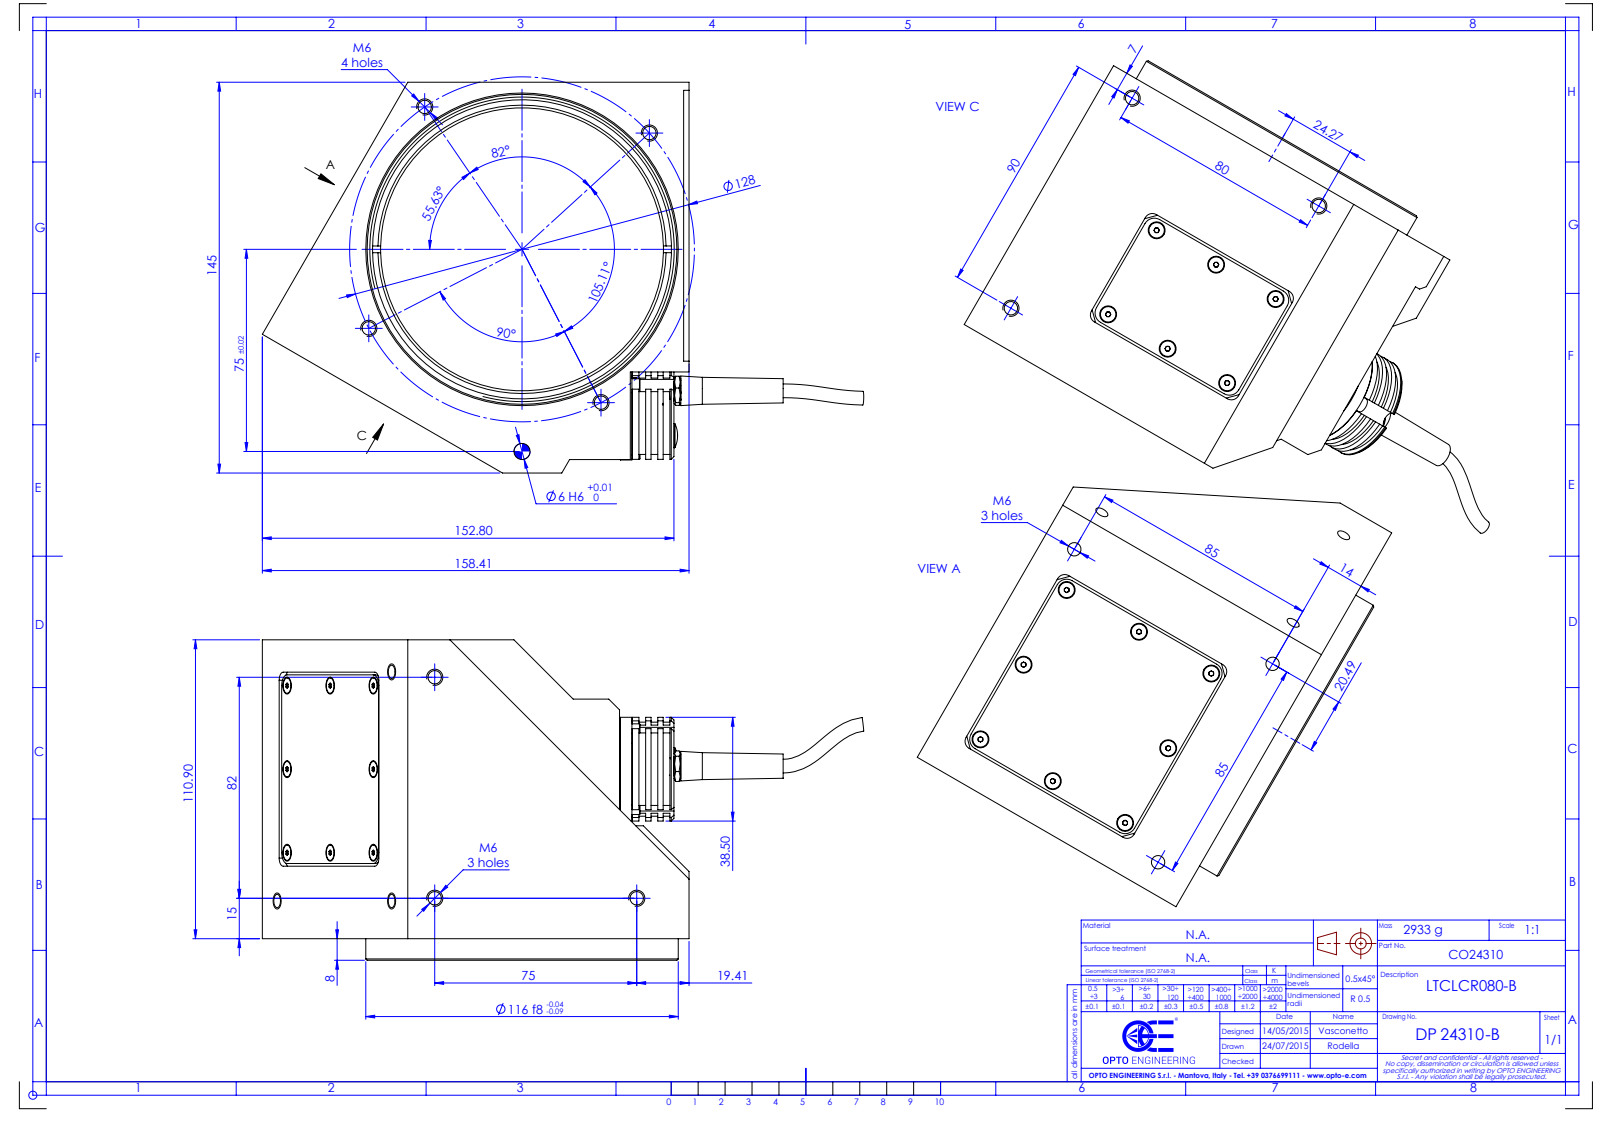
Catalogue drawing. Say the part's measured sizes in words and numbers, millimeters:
The part is named "DP24310-B_LTCLCR080-B". Its 3-D file was written by "SolidWorks 2021 (CONFIG_CONTROL_DESIGN)". It is 0 solids with 404 faces: 156 planar, 138 cylindrical and 110 other. Overall it measures 223.27 by 145 by 118.9 millimeters. Round holes: 13 of diameter 5, 3 of diameter 4, 1 of diameter 6, 1 of diameter 105, 1 of diameter 111. Round bosses or shafts: 18 of diameter 5.75, 3 of diameter 5.5, 1 of diameter 116, 1 of diameter 38.5, 1 of diameter 34.9, 1 of diameter 9. Partial cylindrical surfaces (rounded edges, fillets, slot ends): 10 of radius 4, 8 of radius 3, 3 of radius 2.9, 1 of radius 3.4. The main face-to-face distances are 0.5, 110.9, 145, 25.8, 103.5, 41.5, 5, 140, 36.5, 4. The hole center spacings are 26.41, 64, 75, 85, 34.46, 63.99, 72.96, 80.
